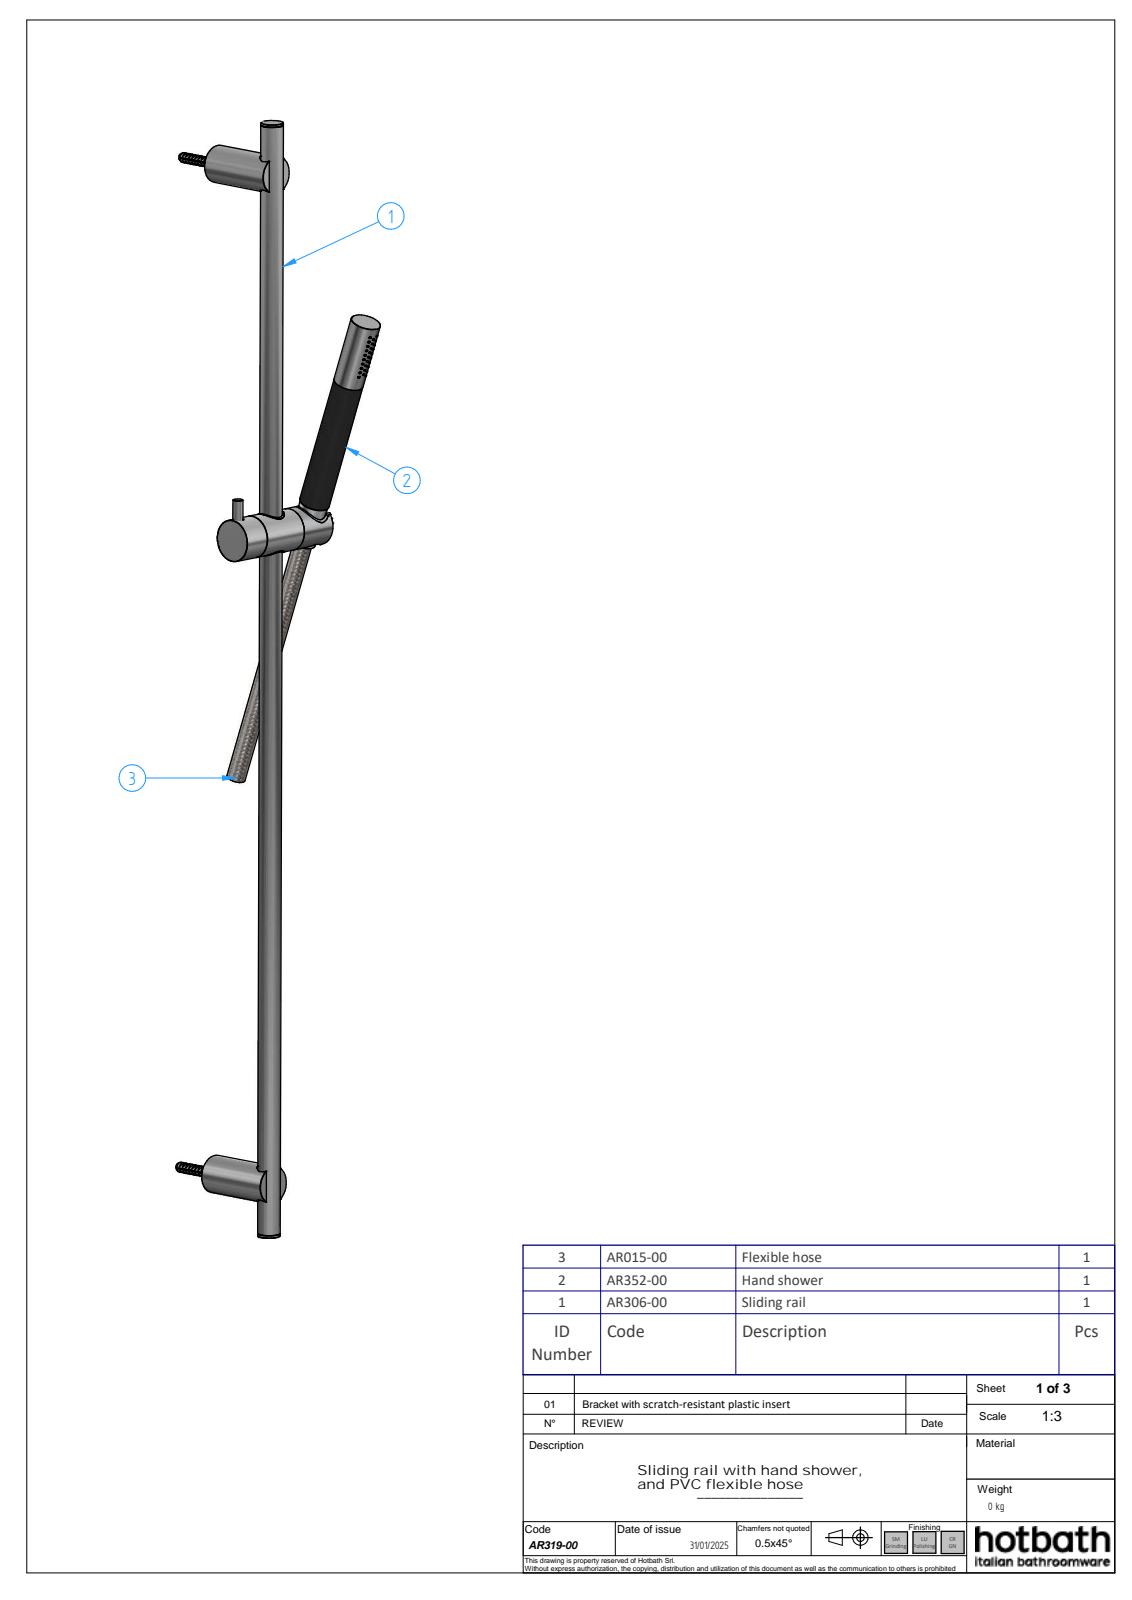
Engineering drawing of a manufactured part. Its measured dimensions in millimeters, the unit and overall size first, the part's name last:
Units: millimetres
Overall size (bounding box): 904 × 160.38 × 98.73
Round holes (diameter × count): ⌀1.2 ×29, ⌀4.13 ×2, ⌀6 ×2, ⌀8 ×2, ⌀12 ×2, ⌀26 ×2, ⌀4.5 ×1, ⌀4.92 ×1, ⌀8.1 ×1, ⌀13.8 ×1, ⌀15.2 ×1, ⌀16 ×1
Round bosses / shafts (diameter × count): ⌀30 ×2, ⌀4 ×2, ⌀33.5 ×1, ⌀30.8 ×1, ⌀24 ×1, ⌀21.8 ×1, ⌀21.1 ×1, ⌀20 ×1
Partial cylindrical surfaces — rounded edges, fillets, slot ends (radius × count): R0.2 ×12, R0.5 ×12, R1.25 ×12, R1.5 ×12, R2 ×10, R1 ×2, R13 ×2, R5.1 ×1
Main face-to-face distances: 2.7, 3, 1.5, 8.5, 67.6, 64.9, 63.5, 6.5, 1.4, 57.4
Hole centre spacings: 4, 8, 12, 16, 24, 20, 20.01, 12.01
Volume: 227 617 mm³ · Surface area: 183 291 mm²
Bodies: 17 solids, 587 faces (172 planar, 240 cylindrical, 175 other)
Part name (STEP PRODUCT): AR319-00 Rel1; AR306-00 Rel1_oa_0; AR307-01; AR307-02 (+8 more)
STEP written by: Solid Edge (AUTOMOTIVE_DESIGN)
